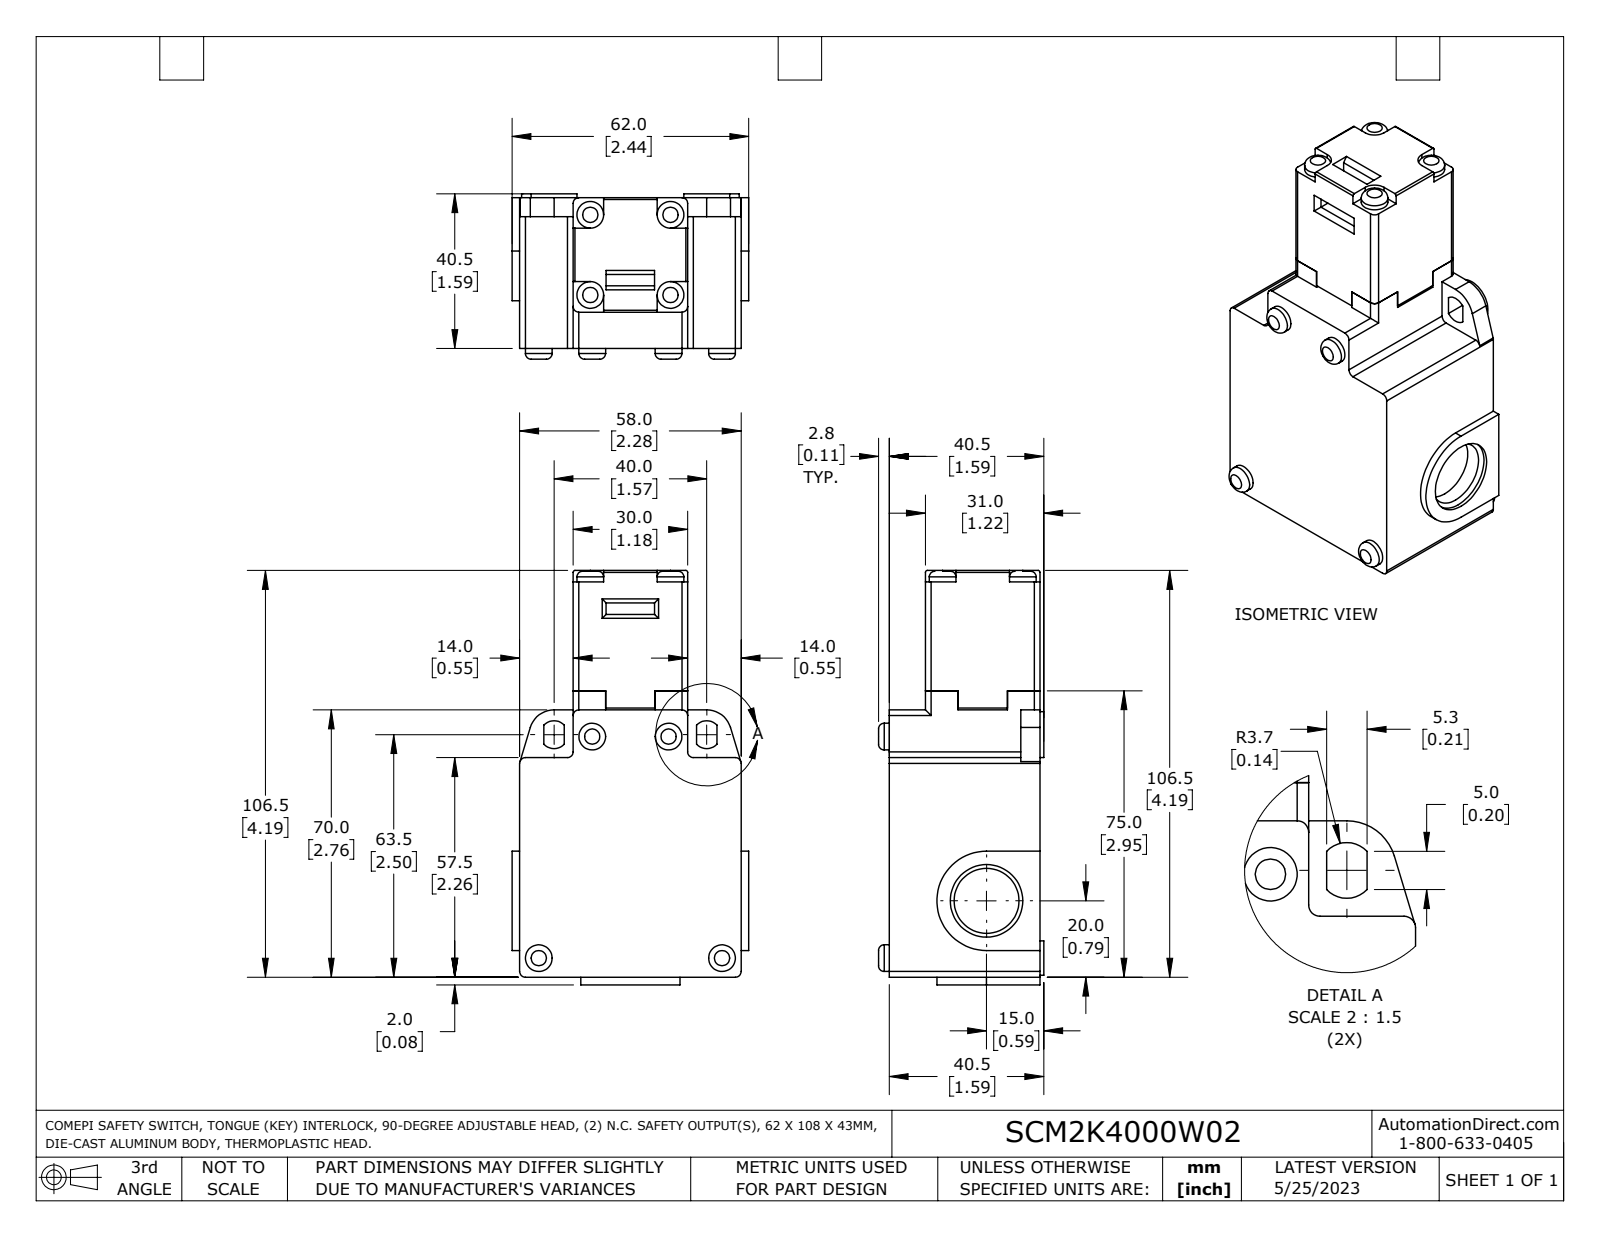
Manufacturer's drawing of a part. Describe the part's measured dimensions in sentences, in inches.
The part is named "SCM2K4000W02". Its 3-D file was written by "SolidWorks 2021 (CONFIG_CONTROL_DESIGN)". It is 2 solids with 176 faces: 106 planar, 59 cylindrical and 11 other. Overall it measures 4.272 by 2.441 by 1.705 inches. Its volume is 10.84 cubic inches and its surface area 43.53 square inches. Round holes: 4 of diameter 0.276, 2 of diameter 0.669, 2 of diameter 0.748. Round bosses or shafts: 4 of diameter 0.276, 2 of diameter 0.472, 2 of diameter 0.354. Partial cylindrical surfaces (rounded edges, fillets, slot ends): 12 of radius 0.059, 4 of radius 0.02, 2 of radius 0.144, 2 of radius 0.256, 2 of radius 0.512, 1 of radius 0.453, 1 of radius 0.472. The main face-to-face distances are 1.555, 1.732, 0.551, 1.181, 2.283, 0.079, 0.236, 0.374, 2.756, 0.118. The hole center spacings are 0.827, 0.557, 0.613, 1.169.
